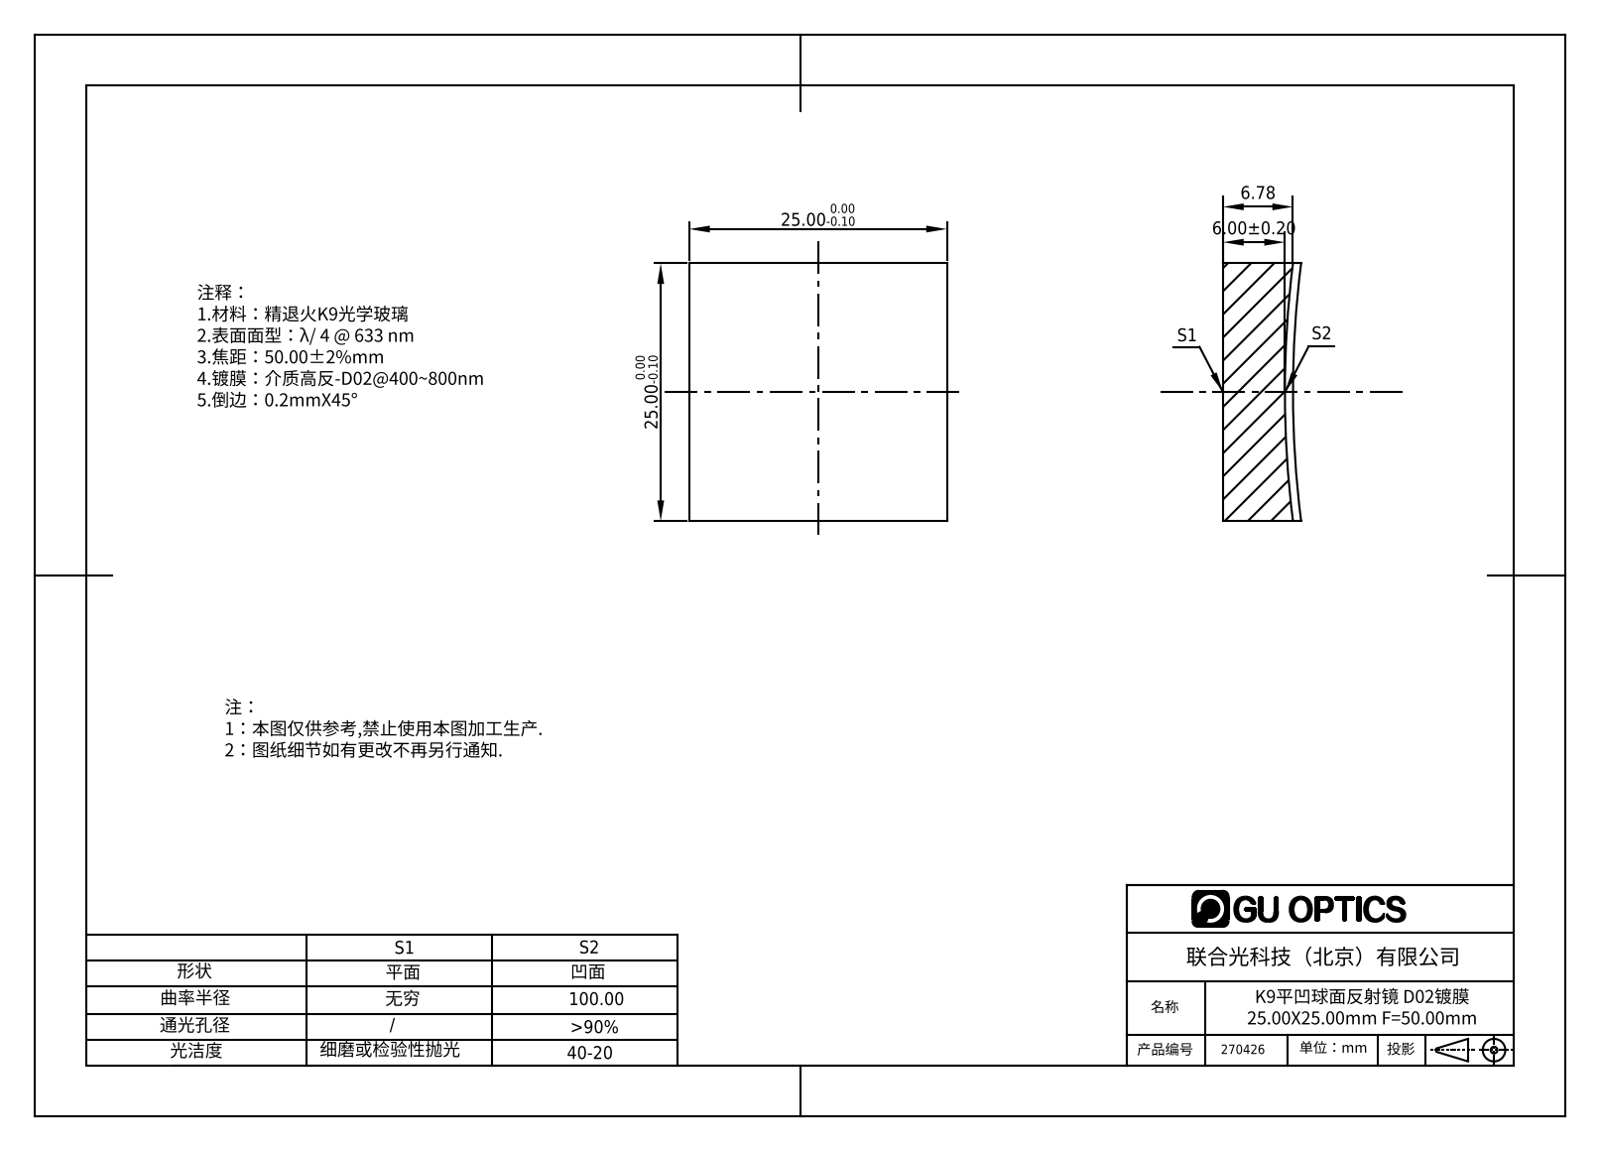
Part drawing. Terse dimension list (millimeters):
name: 270036
written by: SolidWorks 2019 (AUTOMOTIVE_DESIGN)
unit: mm
bodies: 1 solid, 7 faces (5 planar, 0 cylindrical, 2 other)
size: 25 × 25 × 7.58
volume: 4 077 mm³; area: 1 958 mm²
face distances: 25
